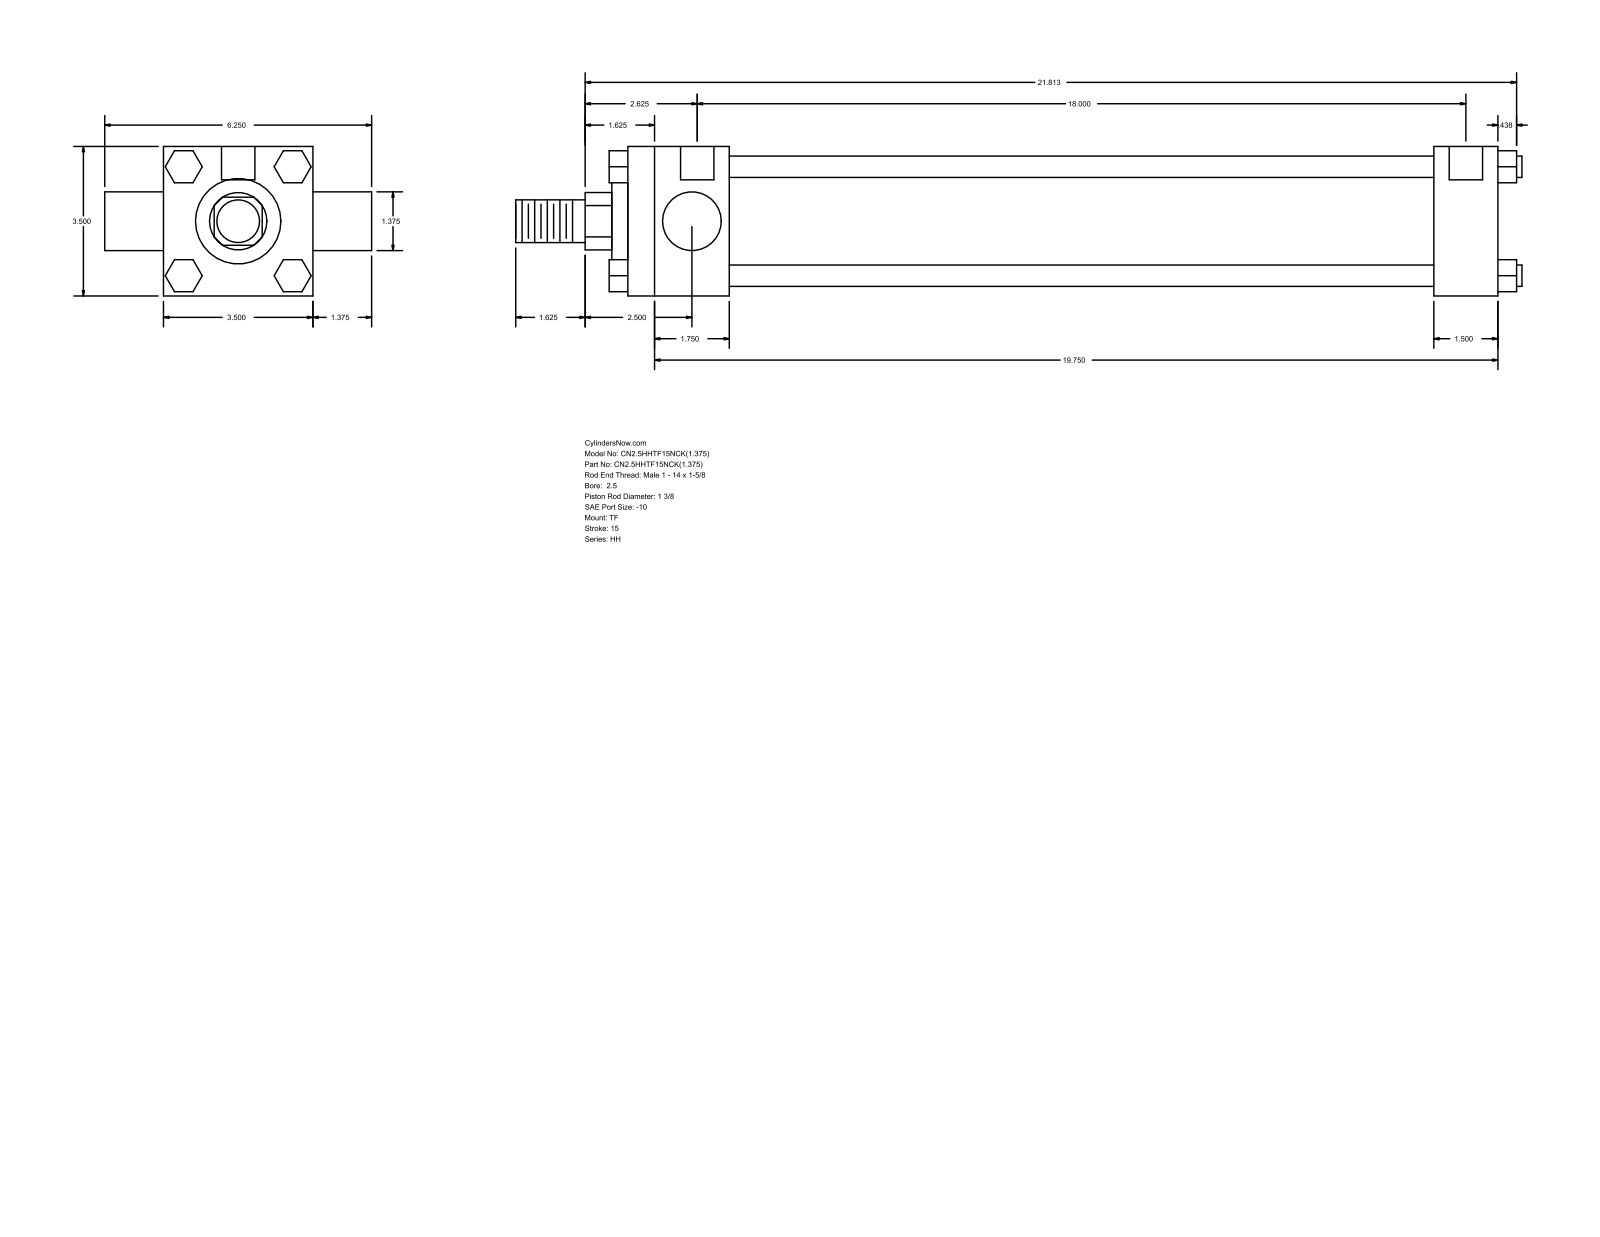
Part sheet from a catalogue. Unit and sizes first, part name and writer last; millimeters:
Units: millimetres
Overall size (bounding box): 598.49 × 158.75 × 88.9
Round holes (diameter × count): ⌀5.56 ×3, ⌀19.84 ×2
Round bosses / shafts (diameter × count): ⌀12.7 ×4, ⌀34.92 ×2, ⌀73.03 ×1, ⌀50.8 ×1, ⌀25.4 ×1
Partial cylindrical surfaces — rounded edges, fillets, slot ends (radius × count): R17.06 ×1
Main face-to-face distances: 88.9, 517.52, 60.32, 457.2, 479.42, 419.1, 38.1, 19.05, 32.38, 56.09
Hole centre spacings: 1.58, 458.79, 457.21, 460.37
Bodies: 0 solids, 120 faces (92 planar, 28 cylindrical, 0 other)
Part name (STEP PRODUCT): HH_TF__0250_1.375
STEP written by: GSSL Pune (CONFIG_CONTROL_DESIGN)
